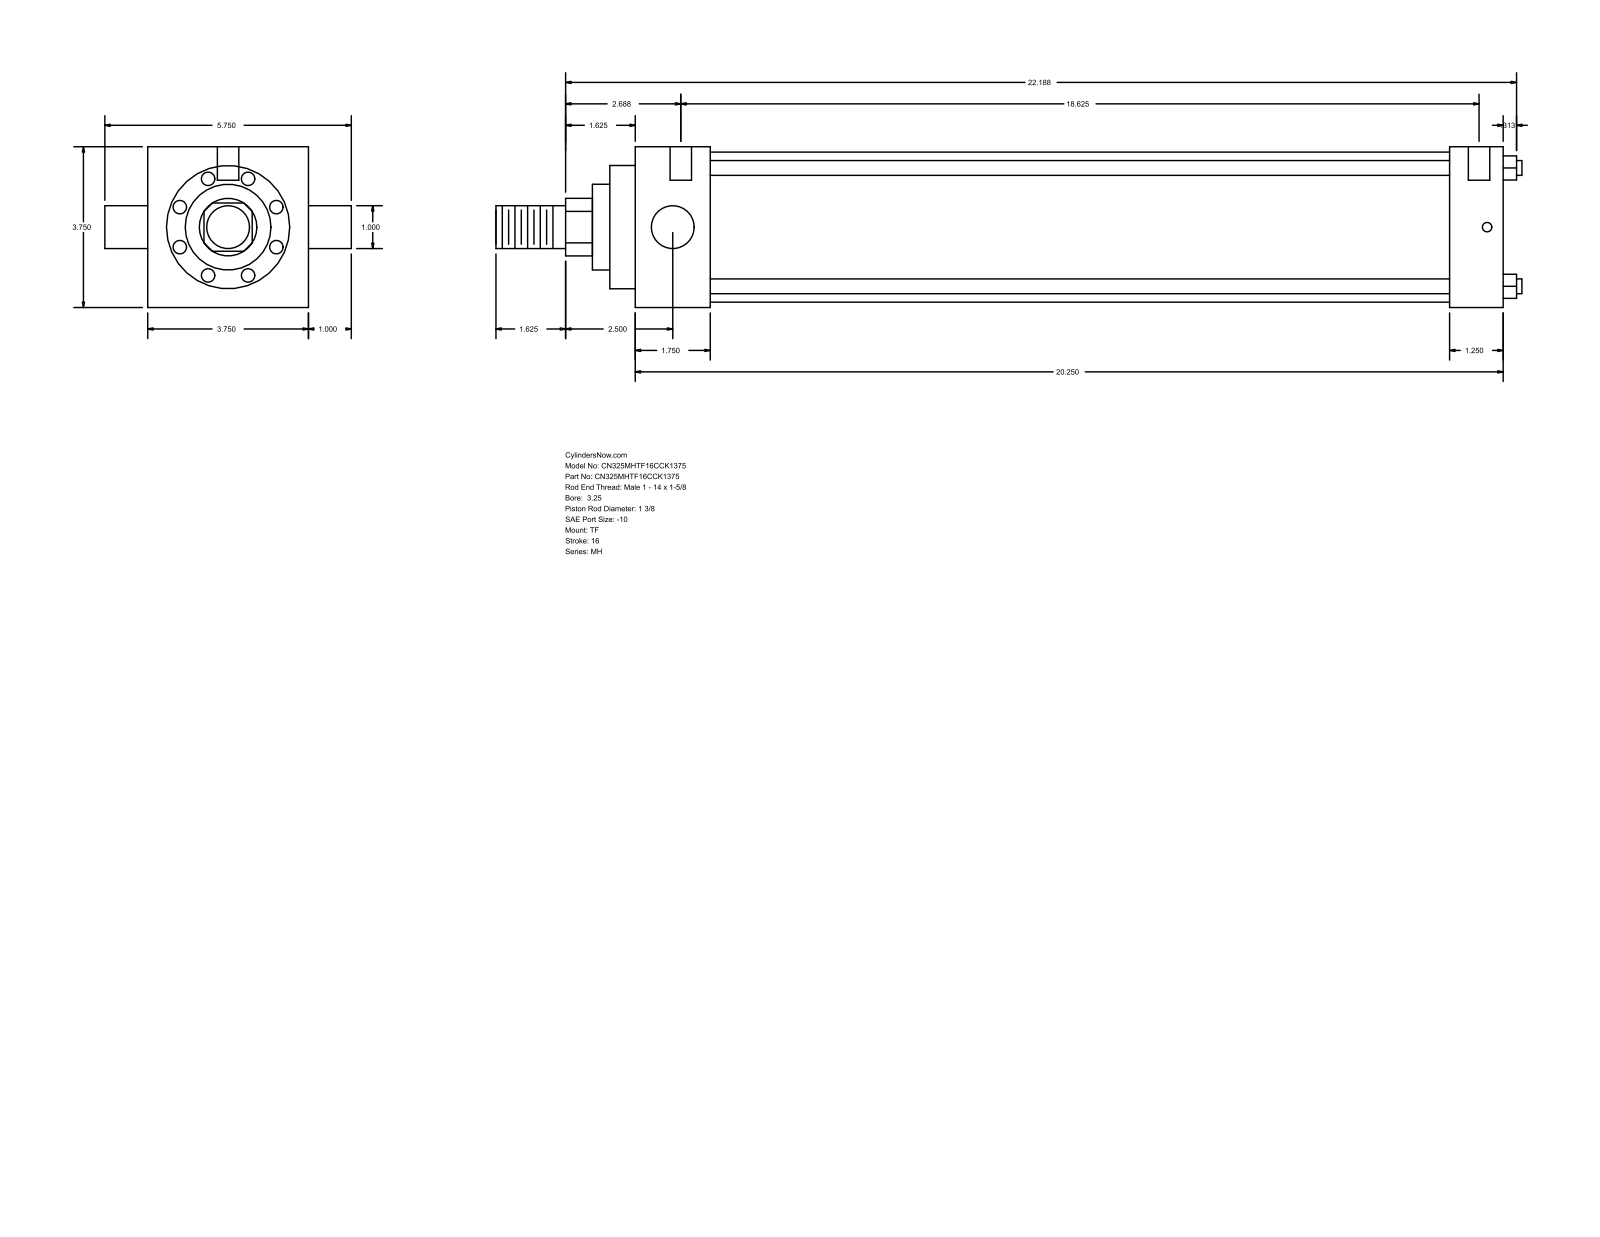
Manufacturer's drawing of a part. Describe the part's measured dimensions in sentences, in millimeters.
The part is named "MH_TF__0325_1.375". Its 3-D file was written by "GSSL Pune (CONFIG_CONTROL_DESIGN)". It is 0 solids with 86 faces: 61 planar, 25 cylindrical and 0 other. Overall it measures 608.01 by 146.05 by 95.25 millimeters. Round holes: 3 of diameter 5.56, 2 of diameter 12.7. Round bosses or shafts: 4 of diameter 8.76, 2 of diameter 25.4, 1 of diameter 88.9, 1 of diameter 73.03, 1 of diameter 50.8, 1 of diameter 34.92. Partial cylindrical surfaces (rounded edges, fillets, slot ends): 1 of radius 17.06. The main face-to-face distances are 95.24, 514.35, 44.45, 482.61, 438.16, 469.9, 31.74, 15.08, 59.53, 497.69. The hole center spacings are 1.59, 4.76, 473.08, 474.67, 477.84, 479.43.
